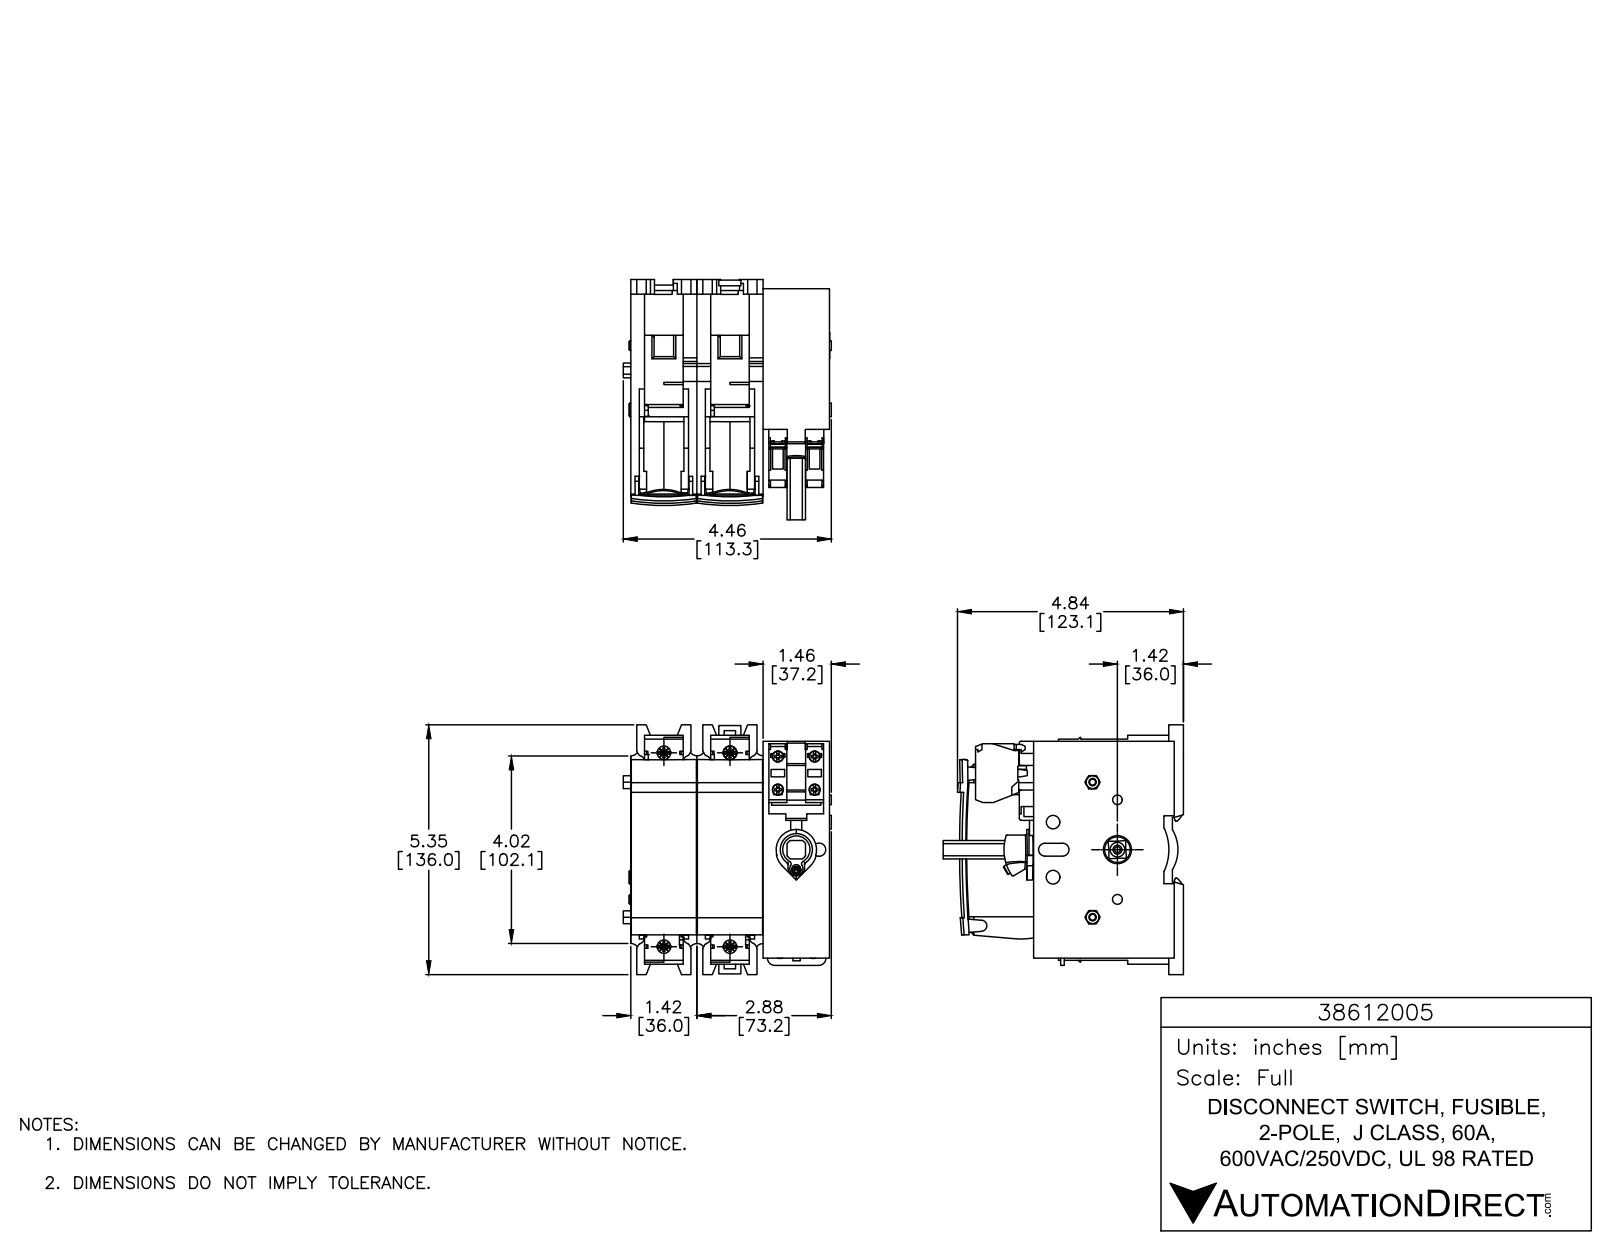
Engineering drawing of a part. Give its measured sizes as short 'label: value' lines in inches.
name: 38612005
written by: SolidWorks 2015 (AUTOMOTIVE_DESIGN)
unit: in
bodies: 9 solids, 1582 faces (1050 planar, 350 cylindrical, 182 other)
size: 5.354 × 4.845 × 4.614
volume: 67.66 in³; area: 253.4 in²
holes: 4× ⌀0.291, 2× ⌀0.087, 2× ⌀0.126, 2× ⌀0.157, 2× ⌀0.158, 2× ⌀0.169, 2× ⌀0.211, 2× ⌀0.295, 2× ⌀0.315, 1× ⌀0.098, 1× ⌀0.13, 1× ⌀0.283
bosses: 2× ⌀0.287, 2× ⌀0.203, 1× ⌀0.63, 1× ⌀0.315, 1× ⌀0.197, 1× ⌀0.139
rounds: 52× R0.006, 12× R0.02, 9× R0.039, 5× R0.197, 4× R0.118, 3× R0.138, 2× R0.065, 2× R0.157
face distances: 1.417, 2.835, 0.295, 1.122, 1.425, 2.843, 4.26, 0.181, 2.539, 1.713
hole spacings: 0.653, 0.987, 1.067, 1.204, 1.342, 1.417, 1.458, 1.499
